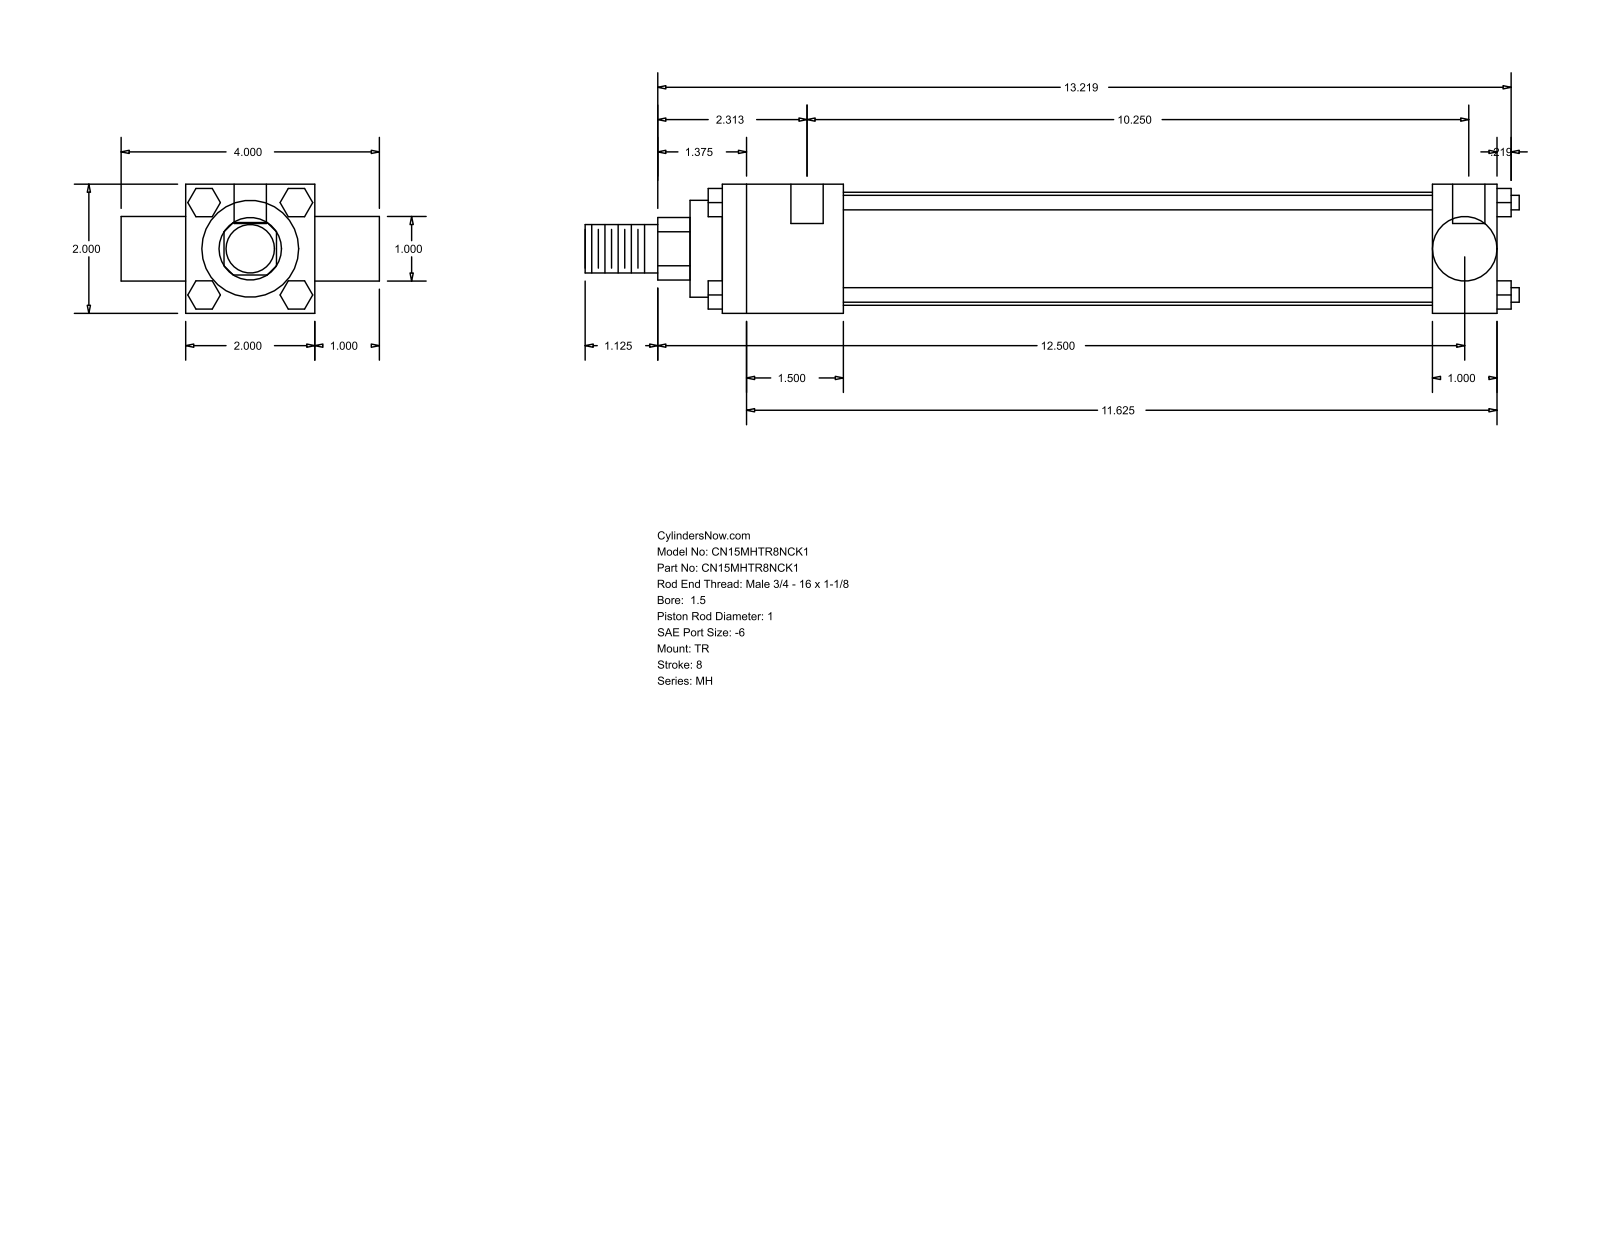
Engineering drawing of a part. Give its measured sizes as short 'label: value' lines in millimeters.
name: MH_TR__0150_1
written by: GSSL Pune (CONFIG_CONTROL_DESIGN)
unit: mm
bodies: 0 solids, 120 faces (92 planar, 28 cylindrical, 0 other)
size: 367.51 × 101.6 × 50.8
holes: 3× ⌀5.56, 2× ⌀12.7
bosses: 4× ⌀5.71, 1× ⌀44.45, 1× ⌀38.1, 1× ⌀25.4, 1× ⌀25.35, 1× ⌀19.05
rounds: 1× R12.29
face distances: 50.8, 25.4, 304.8, 76.2, 47.63, 257.17, 279.4, 231.77, 101.6, 12.7
hole spacings: 3.18, 260.35, 263.53
